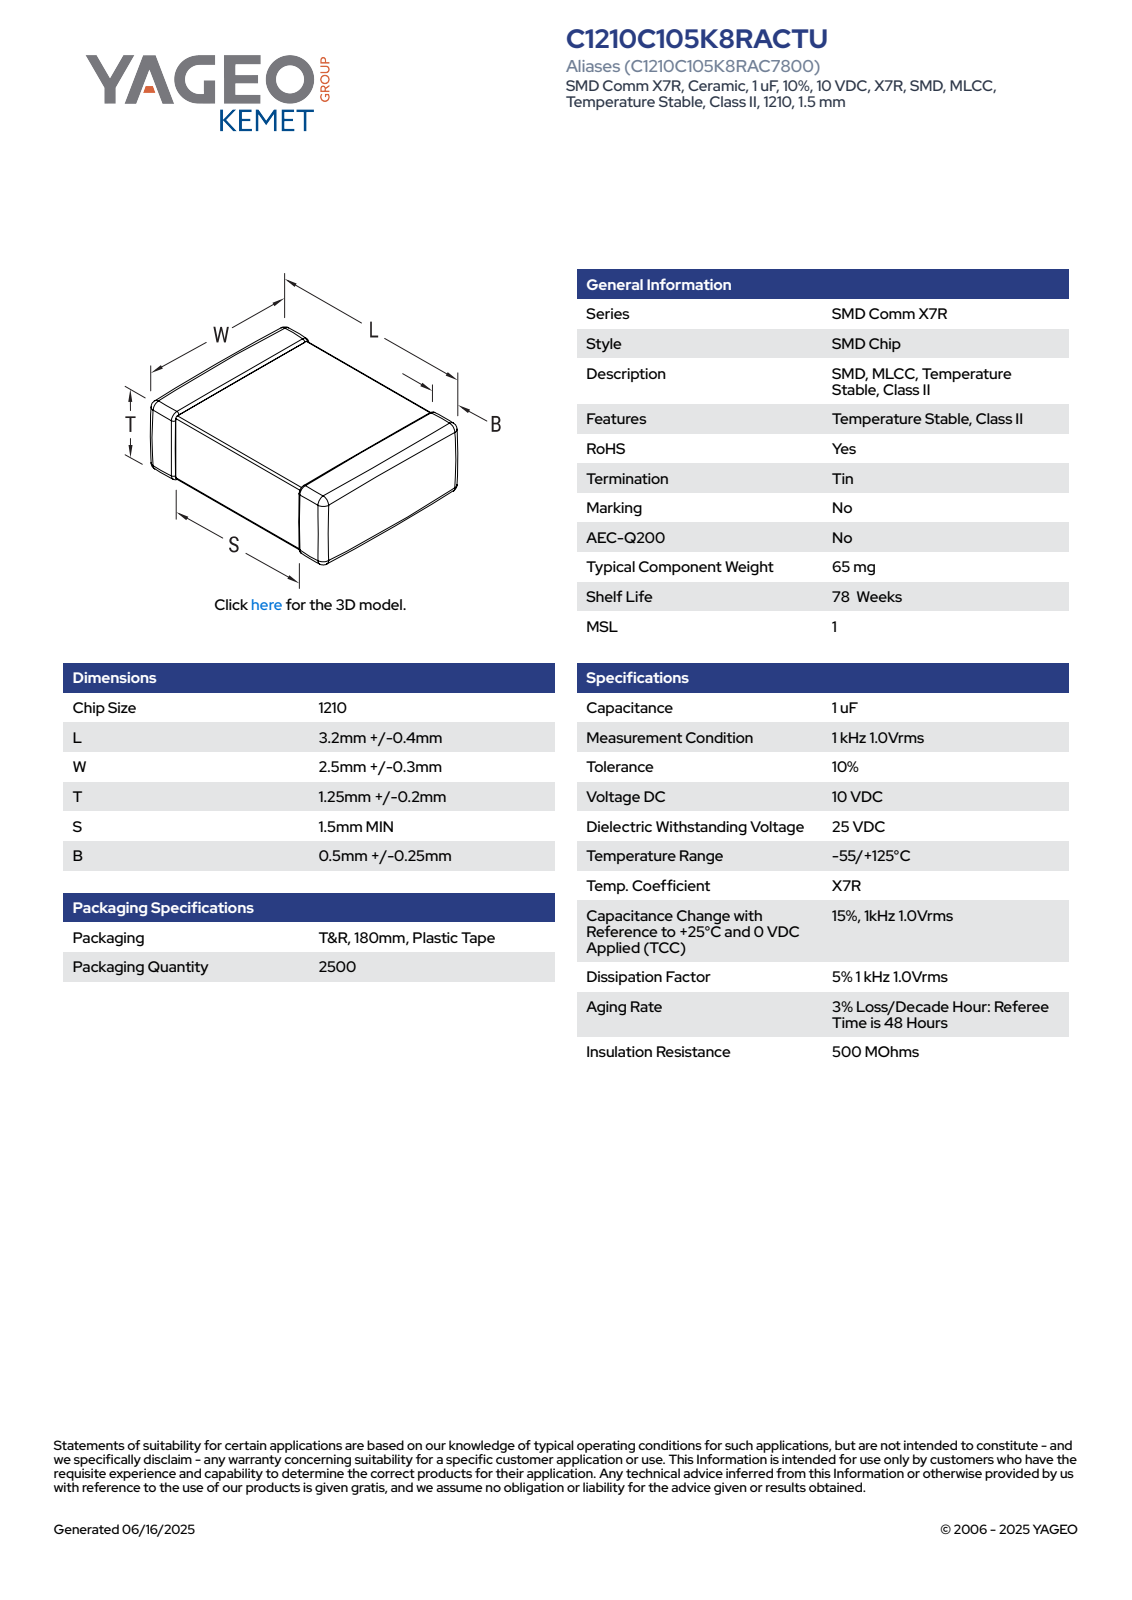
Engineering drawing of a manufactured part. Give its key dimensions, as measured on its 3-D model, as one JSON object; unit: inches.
{"part_name": "CCS_CCSTDNOS_1210_L3.6W2.8T1.45B0.75", "step_written_by": "SolidWorks 2021 (AUTOMOTIVE_DESIGN)", "units": "inches", "bodies": {"solids": 4, "faces": 125, "planar": 71, "cylindrical": 38, "other": 16}, "overall_size": [0.142, 0.11, 0.057], "volume_in3": 0.001, "surface_area_in2": 0.059, "face_to_face_distances": [0.055, 0.052, 0.142, 0.057, 0.108, 0.106, 0.11, 0.055, 0.053, 0.053]}
